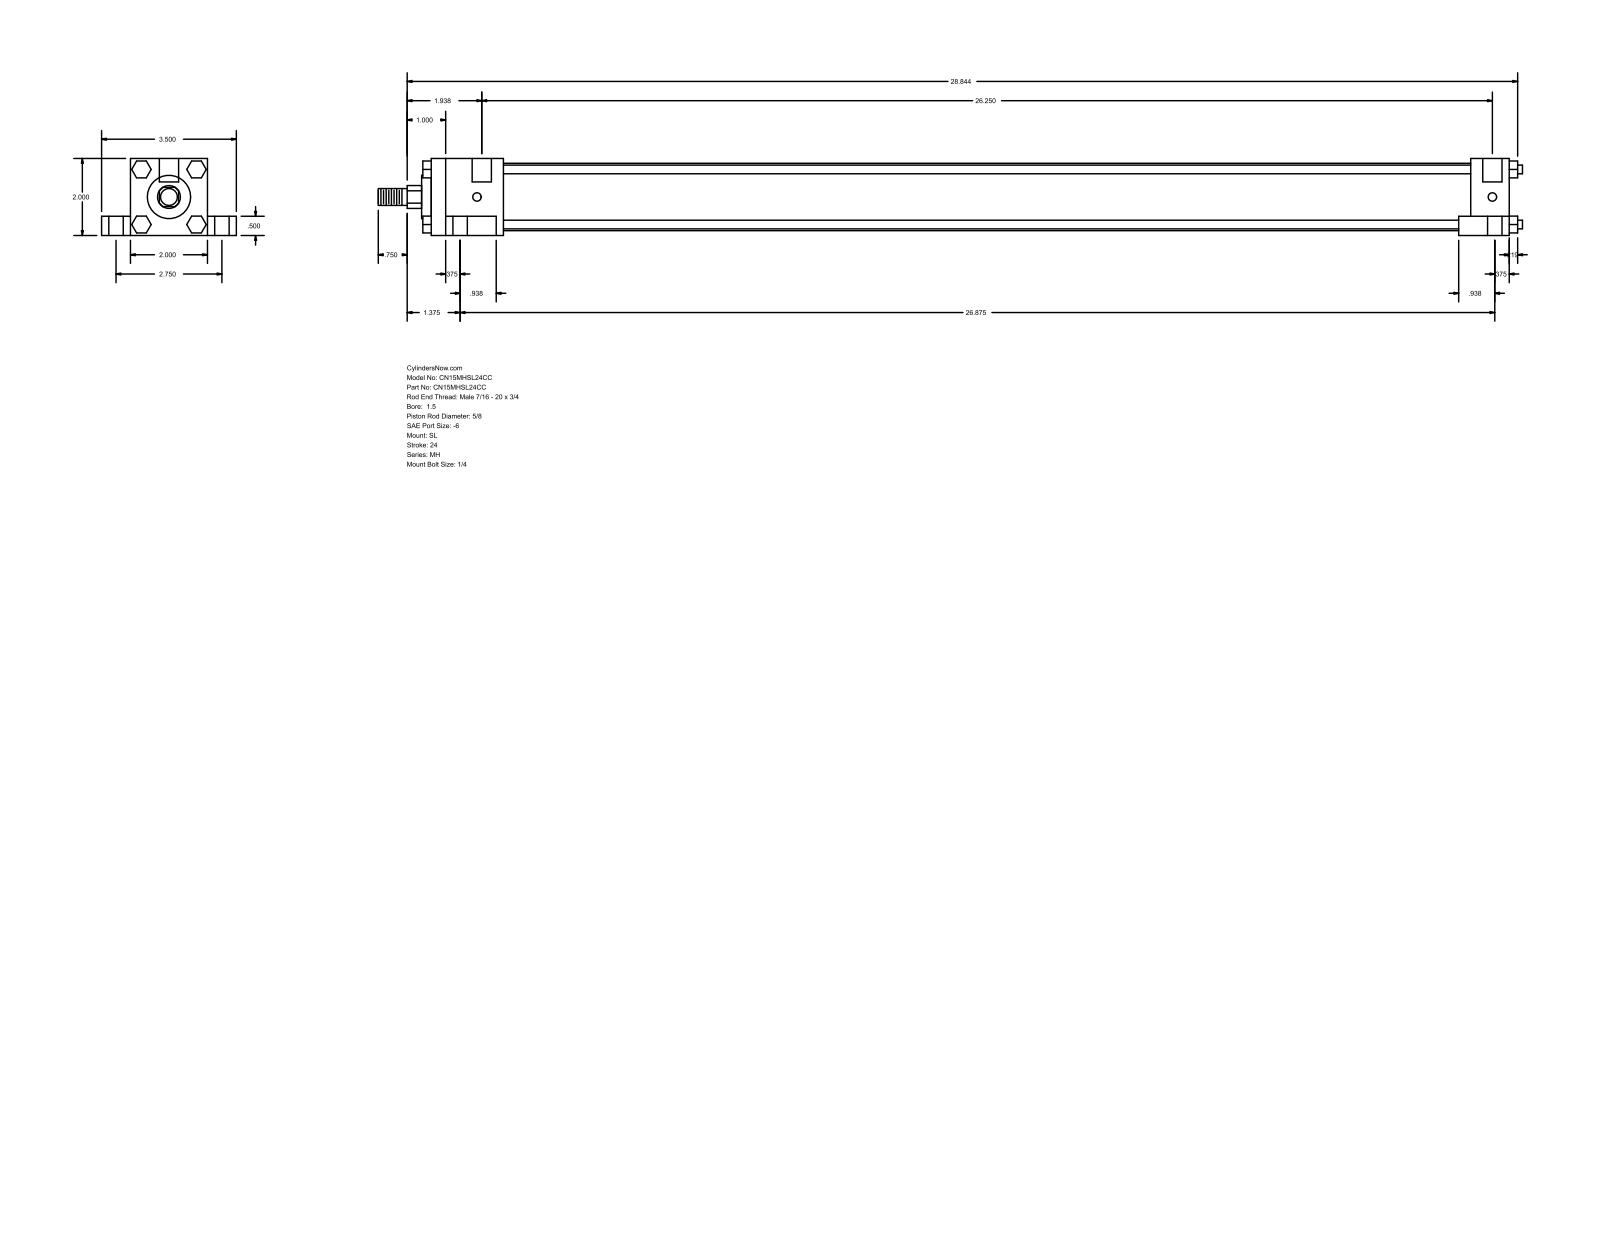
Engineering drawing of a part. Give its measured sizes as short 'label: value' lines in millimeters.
name: MH_SL__0150_0.625
written by: GSSL Pune (CONFIG_CONTROL_DESIGN)
unit: mm
bodies: 0 solids, 148 faces (112 planar, 36 cylindrical, 0 other)
size: 754.86 × 88.9 × 50.8
holes: 4× ⌀5.56, 4× ⌀9.53, 4× ⌀15.88, 2× ⌀12.7
bosses: 4× ⌀5.71, 1× ⌀44.45, 1× ⌀28.57, 1× ⌀15.88, 1× ⌀11.11
rounds: 1× R7.54
face distances: 50.8, 38.1, 19.05, 12.7, 69.85, 711.2, 9.52, 33.34, 668.34, 685.79
hole spacings: 34.96, 36.65, 37.73, 69.84, 669.25, 669.92, 672.42, 681.93
